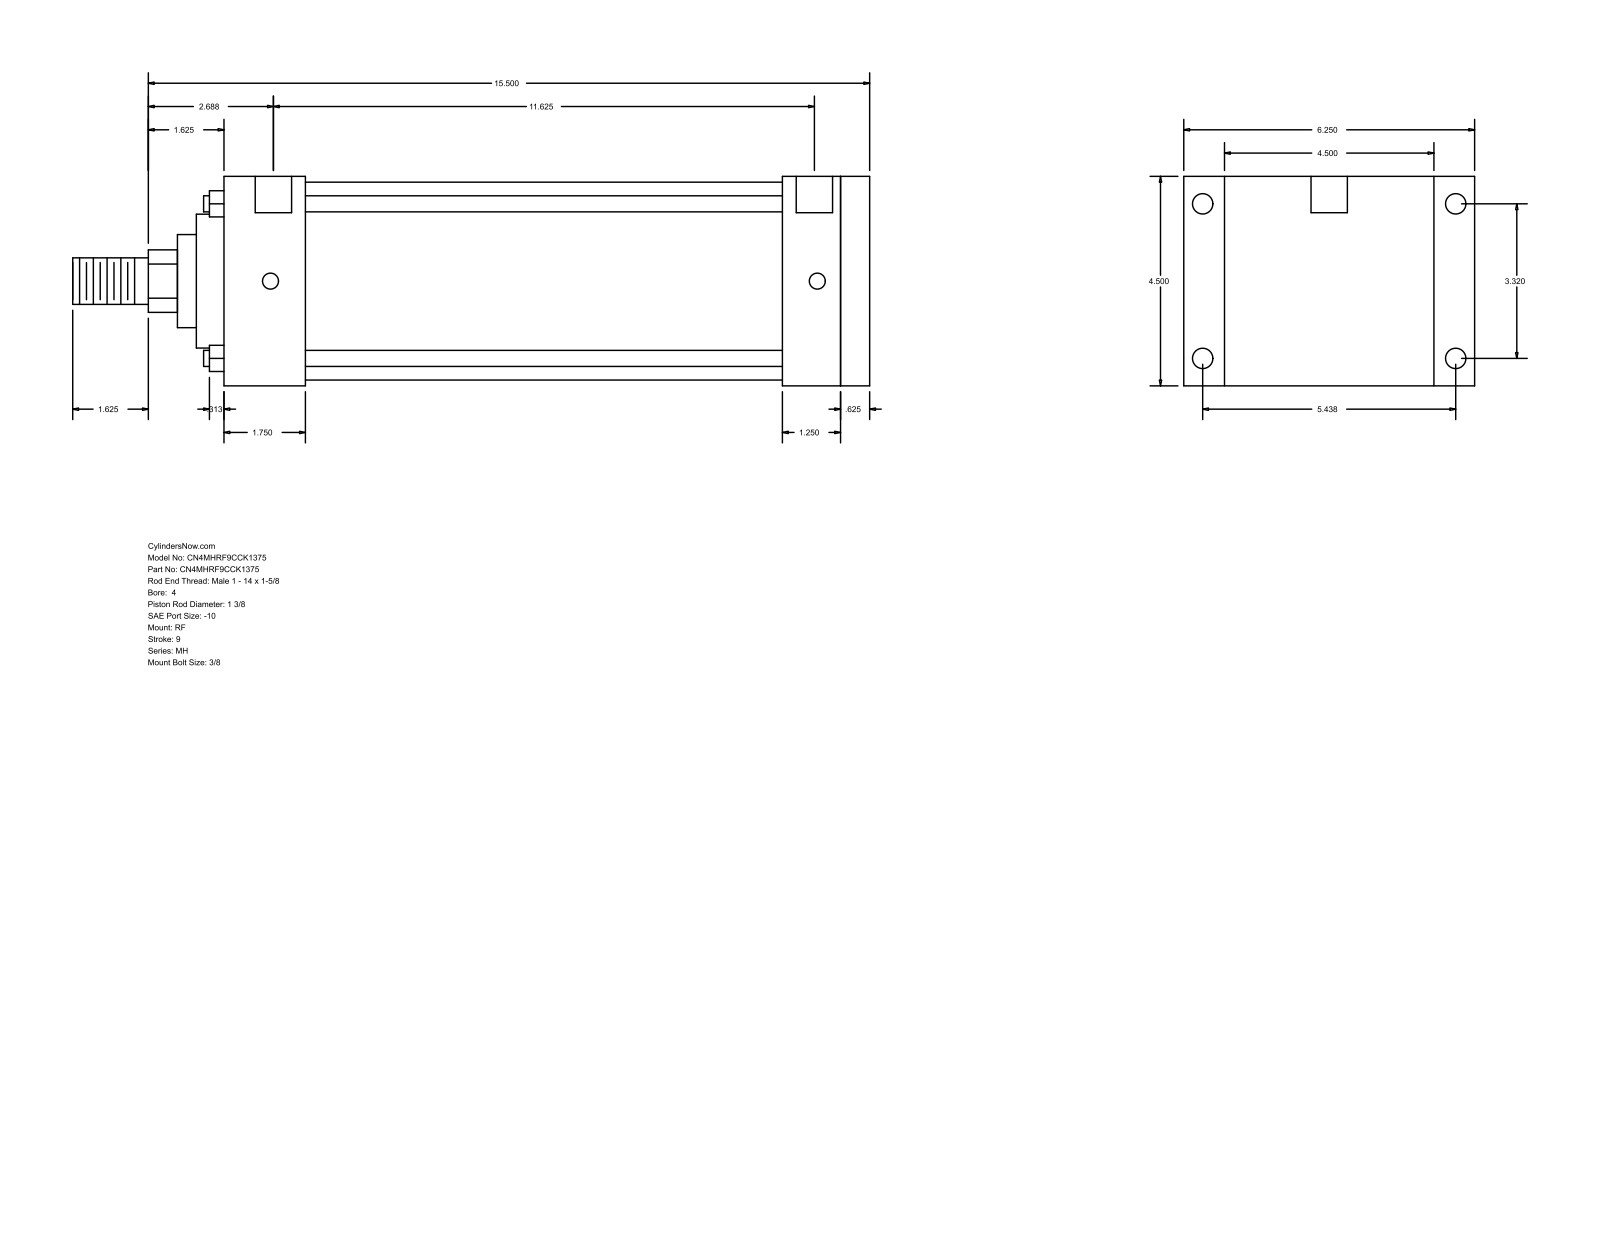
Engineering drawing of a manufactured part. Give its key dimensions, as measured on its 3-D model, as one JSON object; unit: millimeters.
{"part_name": "MH_RF__0400_1.375", "step_written_by": "GSSL Pune (CONFIG_CONTROL_DESIGN)", "units": "millimeters", "bodies": {"solids": 0, "faces": 94, "planar": 65, "cylindrical": 29, "other": 0}, "overall_size": [434.98, 158.75, 114.3], "round_holes": [[8.73, 4], [11.13, 4], [19.84, 2]], "round_bosses_or_shafts": [[8.76, 4], [107.95, 1], [73.03, 1], [50.8, 1], [34.92, 1], [25.4, 1]], "partial_cylinders_radius": [[17.06, 1]], "face_to_face_distances": [114.3, 352.43, 15.88, 336.55, 44.45, 292.1, 307.98, 304.8, 260.35, 31.75], "hole_center_spacings": [84.32, 138.12, 161.82, 298.45, 1.58, 1.59, 295.28, 296.86]}
